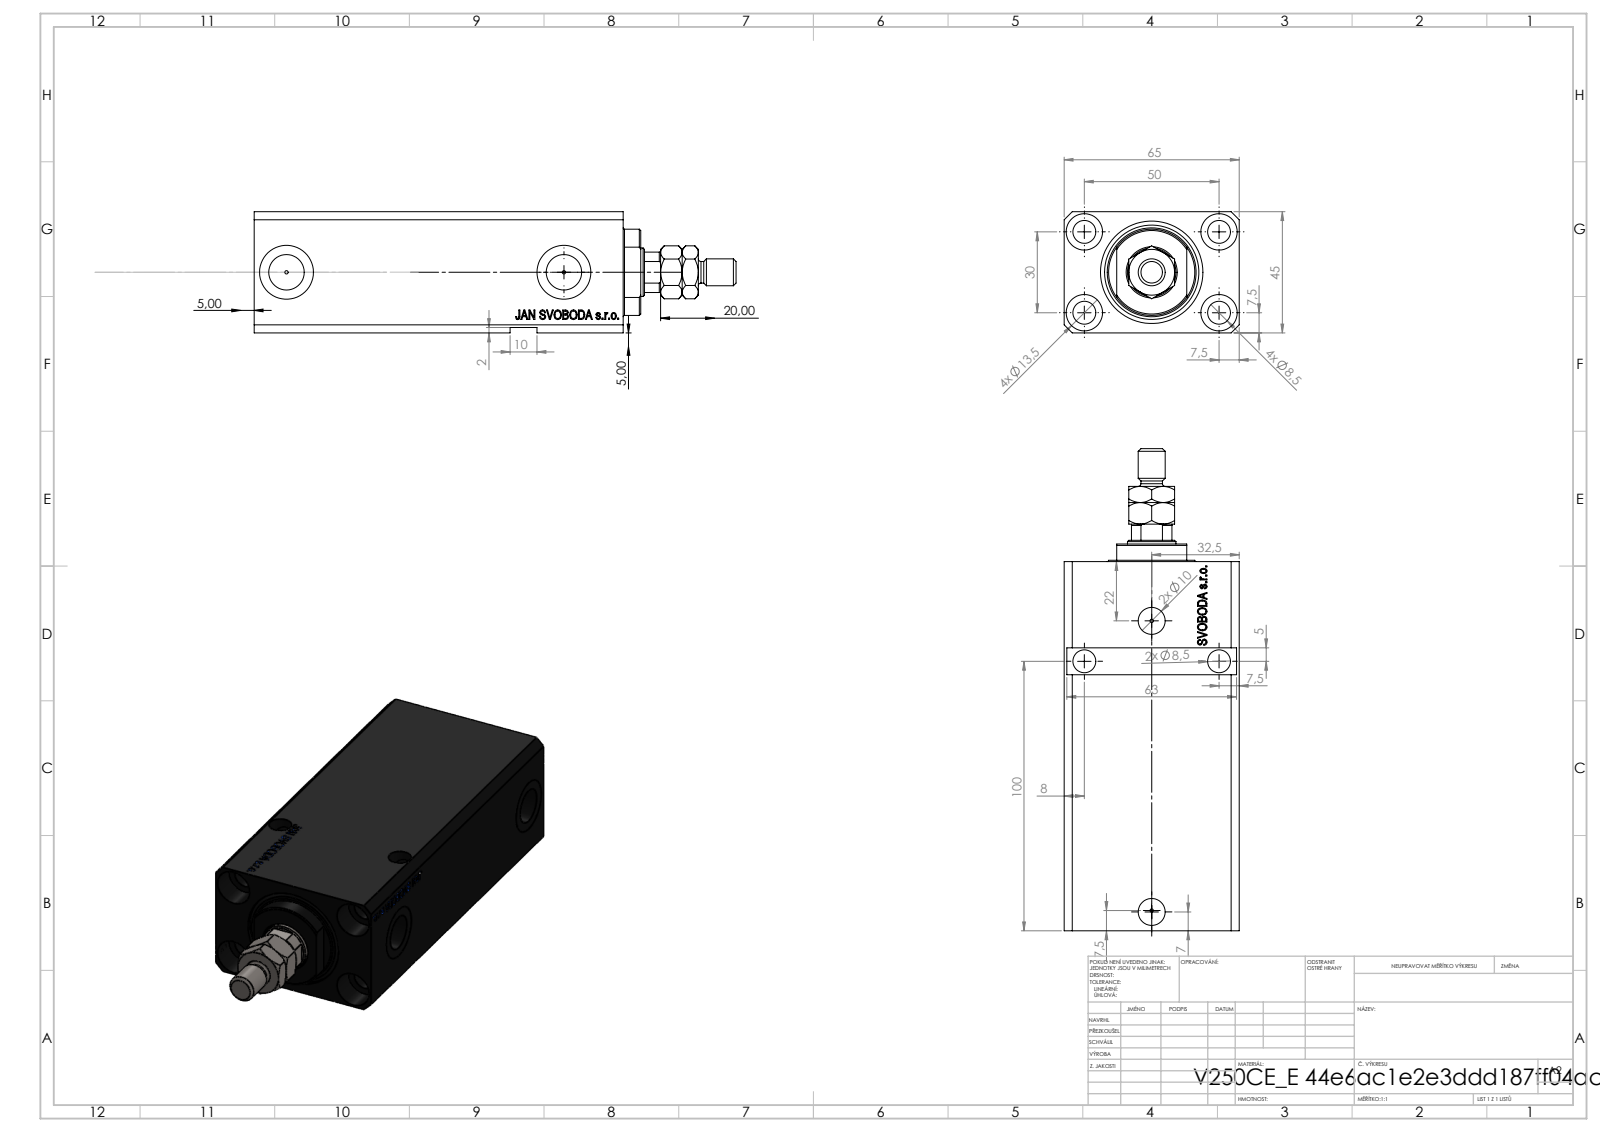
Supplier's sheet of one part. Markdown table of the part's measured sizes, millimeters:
| quantity | value |
| --- | --- |
| part name | MTA; V250CE_VC_E; V250CE_E_Body; V250CE_C_VCP |
| STEP written by | SolidWorks 2019 (CONFIG_CONTROL_DESIGN) |
| units | millimeters |
| bodies | 4 solids, 982 faces (454 planar, 120 cylindrical, 408 other) |
| overall size | 179 × 65 × 45 |
| volume | 335 732 mm³ |
| surface area | 83 446 mm² |
| round holes (diameter × count) | 8.5 × 9, 1.25 × 4, 13.5 × 4, 10 × 2, 13.16 × 2, 20 × 2, 18 × 1, 25 × 1, 38 × 1 |
| round bosses / shafts (diameter × count) | 10 × 1, 8 × 1 |
| partial cylindrical surfaces (radius × count) | 8.5 × 1, 16 × 1 |
| main face-to-face distances | 45, 65, 14, 123, 137, 6.9, 116.1, 130.1, 43, 28 |
| hole center spacings | 29.15, 50, 30, 33.61, 33.97, 58.31, 70, 86.02 |
